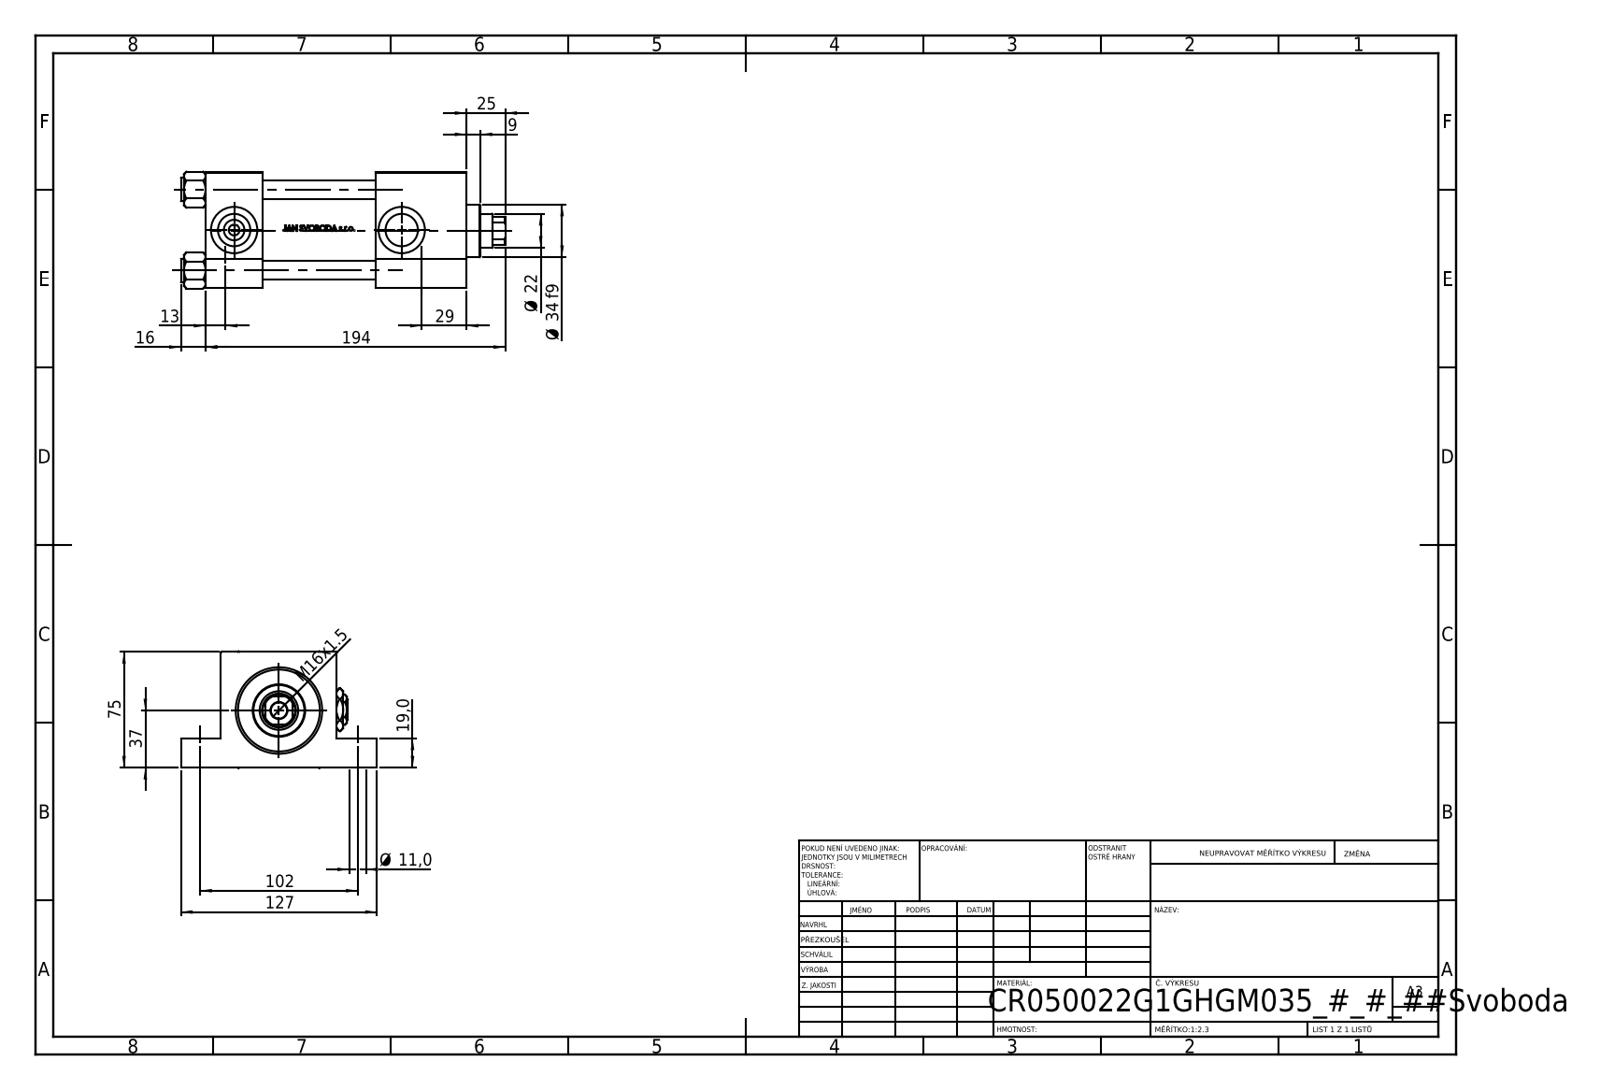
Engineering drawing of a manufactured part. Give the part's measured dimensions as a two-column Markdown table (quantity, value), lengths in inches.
| quantity | value |
| --- | --- |
| part name | Zatka_pro_OIL_PORT; V215CR_G_Body; NUT_M5_G; V215CR_G_TYCINKA (+2 more) |
| STEP written by | SolidWorks 2019 (CONFIG_CONTROL_DESIGN) |
| units | inches |
| bodies | 12 solids, 1134 faces (454 planar, 128 cylindrical, 552 other) |
| overall size | 8.268 × 5 × 2.974 |
| volume | 47.13 in³ |
| surface area | 262.9 in² |
| round holes (diameter × count) | 0.433 × 4, 0.472 × 4, 0.276 × 2, 0.825 × 2, 1.181 × 2, 0.413 × 1, 0.866 × 1, 0.984 × 1, 1.614 × 1, 1.969 × 1, 2.087 × 1 |
| round bosses / shafts (diameter × count) | 0.591 × 4, 2.205 × 1, 1.339 × 1 |
| partial cylindrical surfaces (radius × count) | 0.413 × 1 |
| main face-to-face distances | 2.953, 1.457, 6.654, 5.197, 0.748, 2.205, 4.331, 2.874, 2.323, 1.024 |
| hole center spacings | 2.059, 1.442, 1.47, 2.912, 4.016, 5, 6.413, 4.272 |
